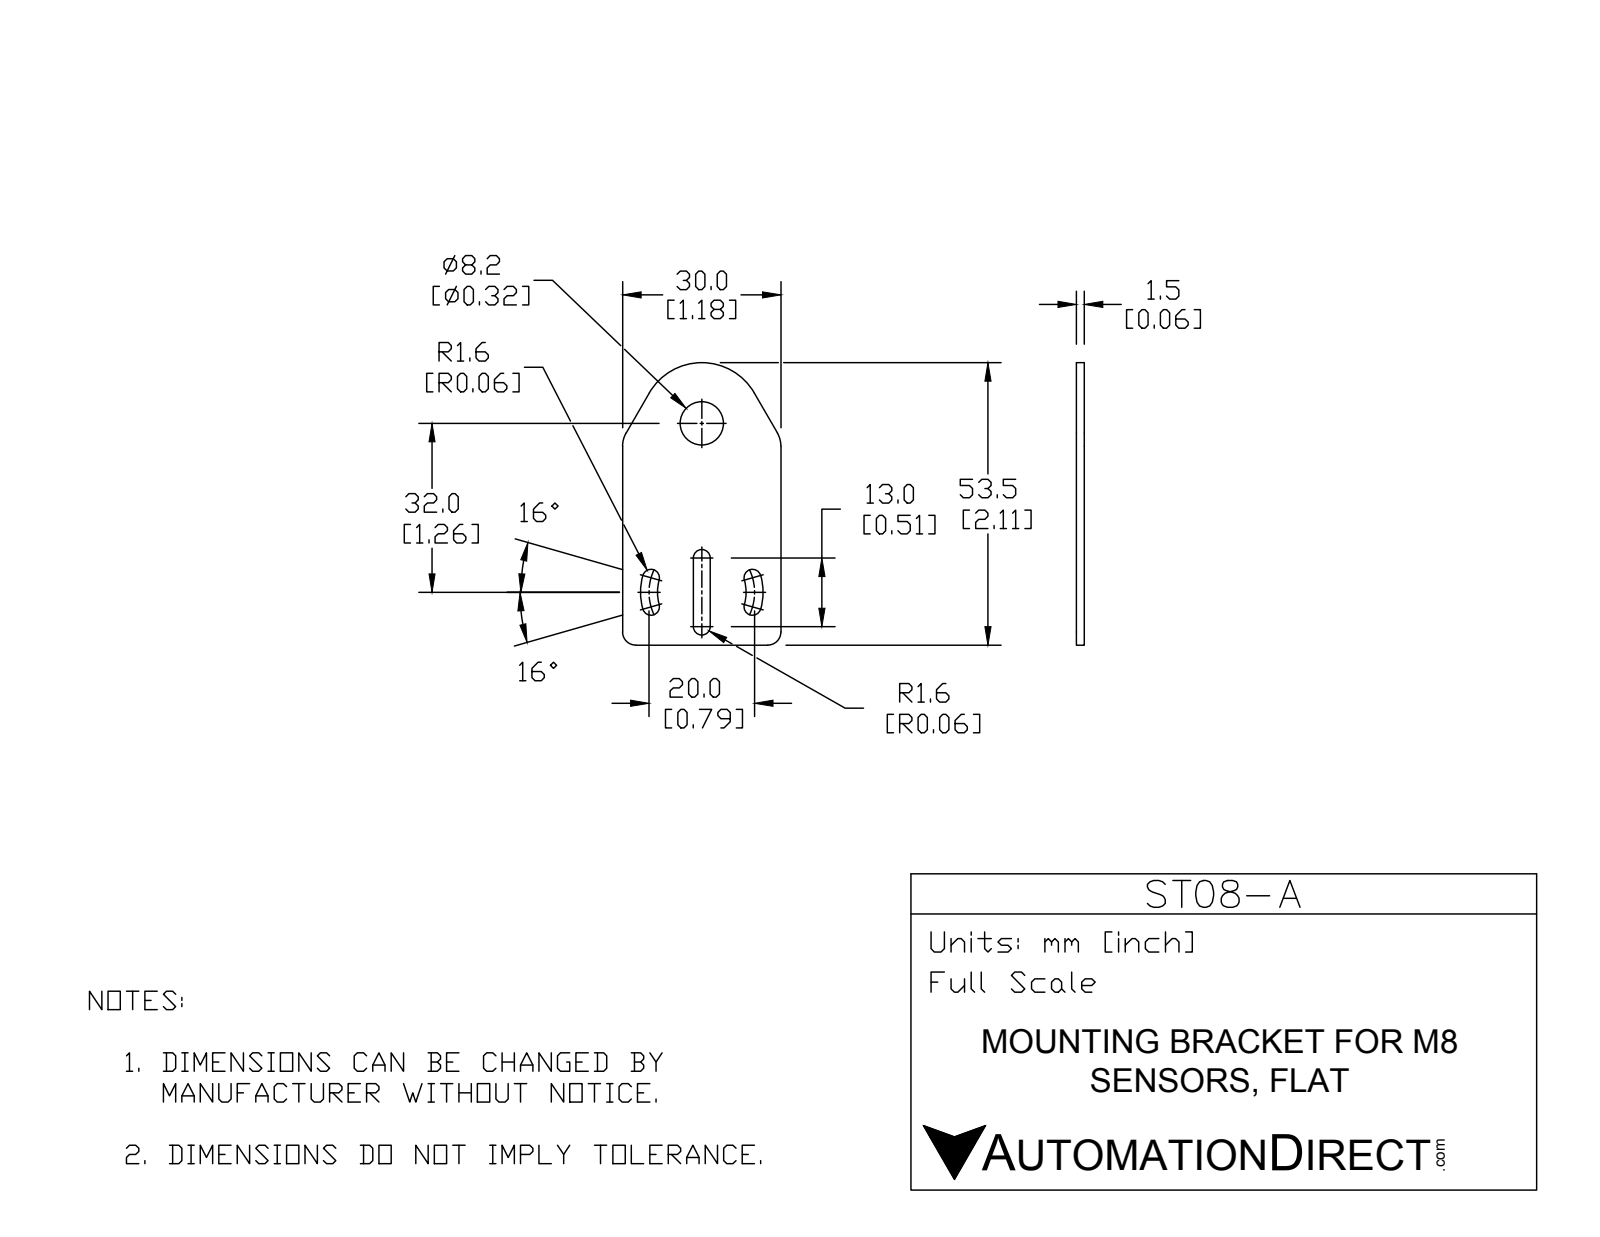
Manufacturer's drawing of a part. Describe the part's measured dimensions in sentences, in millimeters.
The part is named "ST08-A". Its 3-D file was written by "SolidWorks 2015 (CONFIG_CONTROL_DESIGN)". It is 1 solid with 30 faces: 9 planar, 21 cylindrical and 0 other. Overall it measures 53.5 by 30 by 1.5 millimeters. Its volume is 1 970 cubic millimeters and its surface area 3 008 square millimeters. Round holes: 1 of diameter 8.2. Partial cylindrical surfaces (rounded edges, fillets, slot ends): 6 of radius 1.6, 2 of radius 2, 2 of radius 5, 1 of radius 8.4, 1 of radius 11.48, 1 of radius 11.6. The main face-to-face distances are 1.5, 30, 13.4, 16.6, 3.2.
